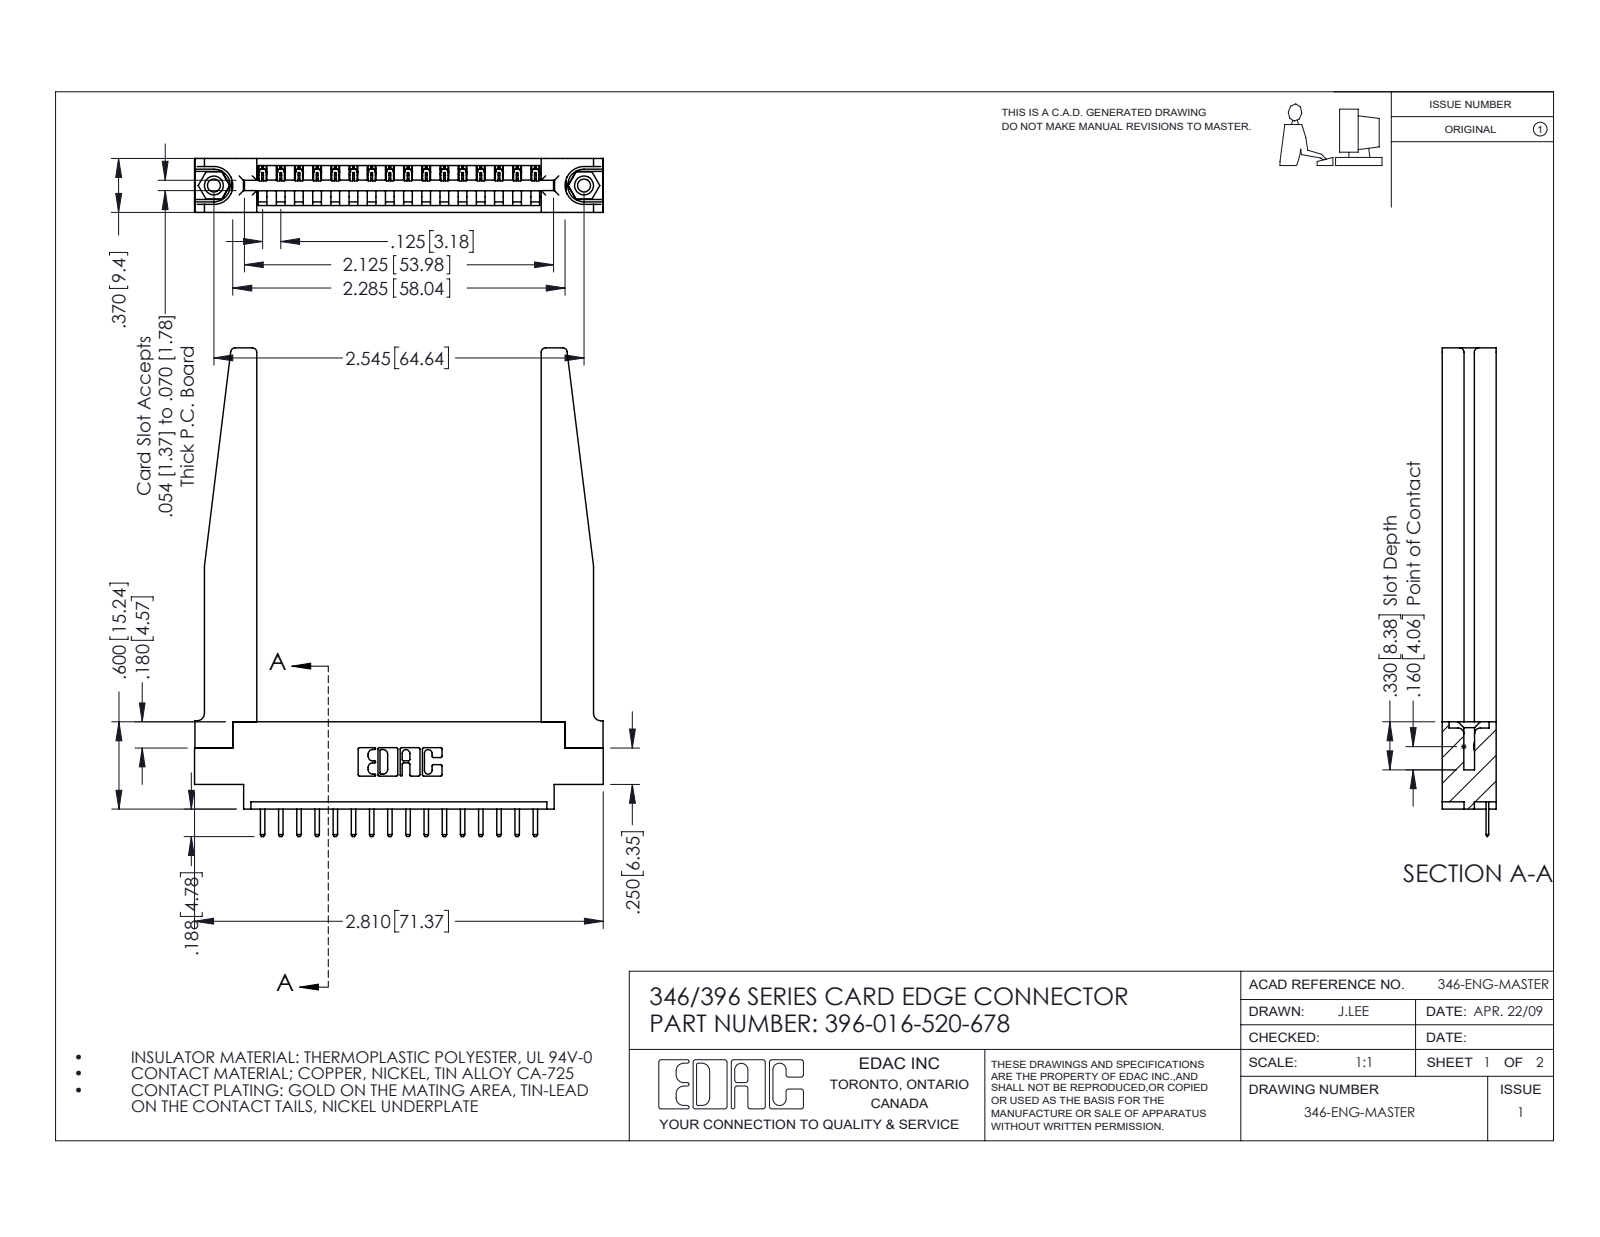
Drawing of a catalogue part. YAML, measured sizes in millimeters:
part_name: "346 Part_0.170 Offset - 0.156 Dia-TH; 396-016-520-678; 345-292-001_345-293-120; 345-250-001_345-250-001-102 (+1 more)"
step_written_by: "SolidWorks 2016 (CONFIG_CONTROL_DESIGN)"
units: millimeters
bodies: {solids: 21, faces: 1352, planar: 894, cylindrical: 406, other: 52}
overall_size: [85.3, 71.4, 9.4]
volume: 13400
surface_area: 14330
round_holes:
  - {diameter: 2.3, count: 2}
  - {diameter: 3.2, count: 2}
  - {diameter: 4, count: 2}
  - {diameter: 1.6, count: 1}
round_bosses_or_shafts:
  - {diameter: 3.9, count: 2}
partial_cylinders:
  - {radius: 0.3, count: 34}
  - {radius: 0.2, count: 32}
  - {radius: 0.3, count: 22}
  - {radius: 0.8, count: 8}
  - {radius: 0.2, count: 6}
  - {radius: 0.8, count: 6}
  - {radius: 0.7, count: 3}
  - {radius: 0.8, count: 2}
face_to_face_distances: [9.4, 3.8, 1.8, 3.8, 1.2, 8.2, 6.4, 2.6, 5.6, 4.4]
hole_center_spacings: [6.2, 59.4, 64.6]
